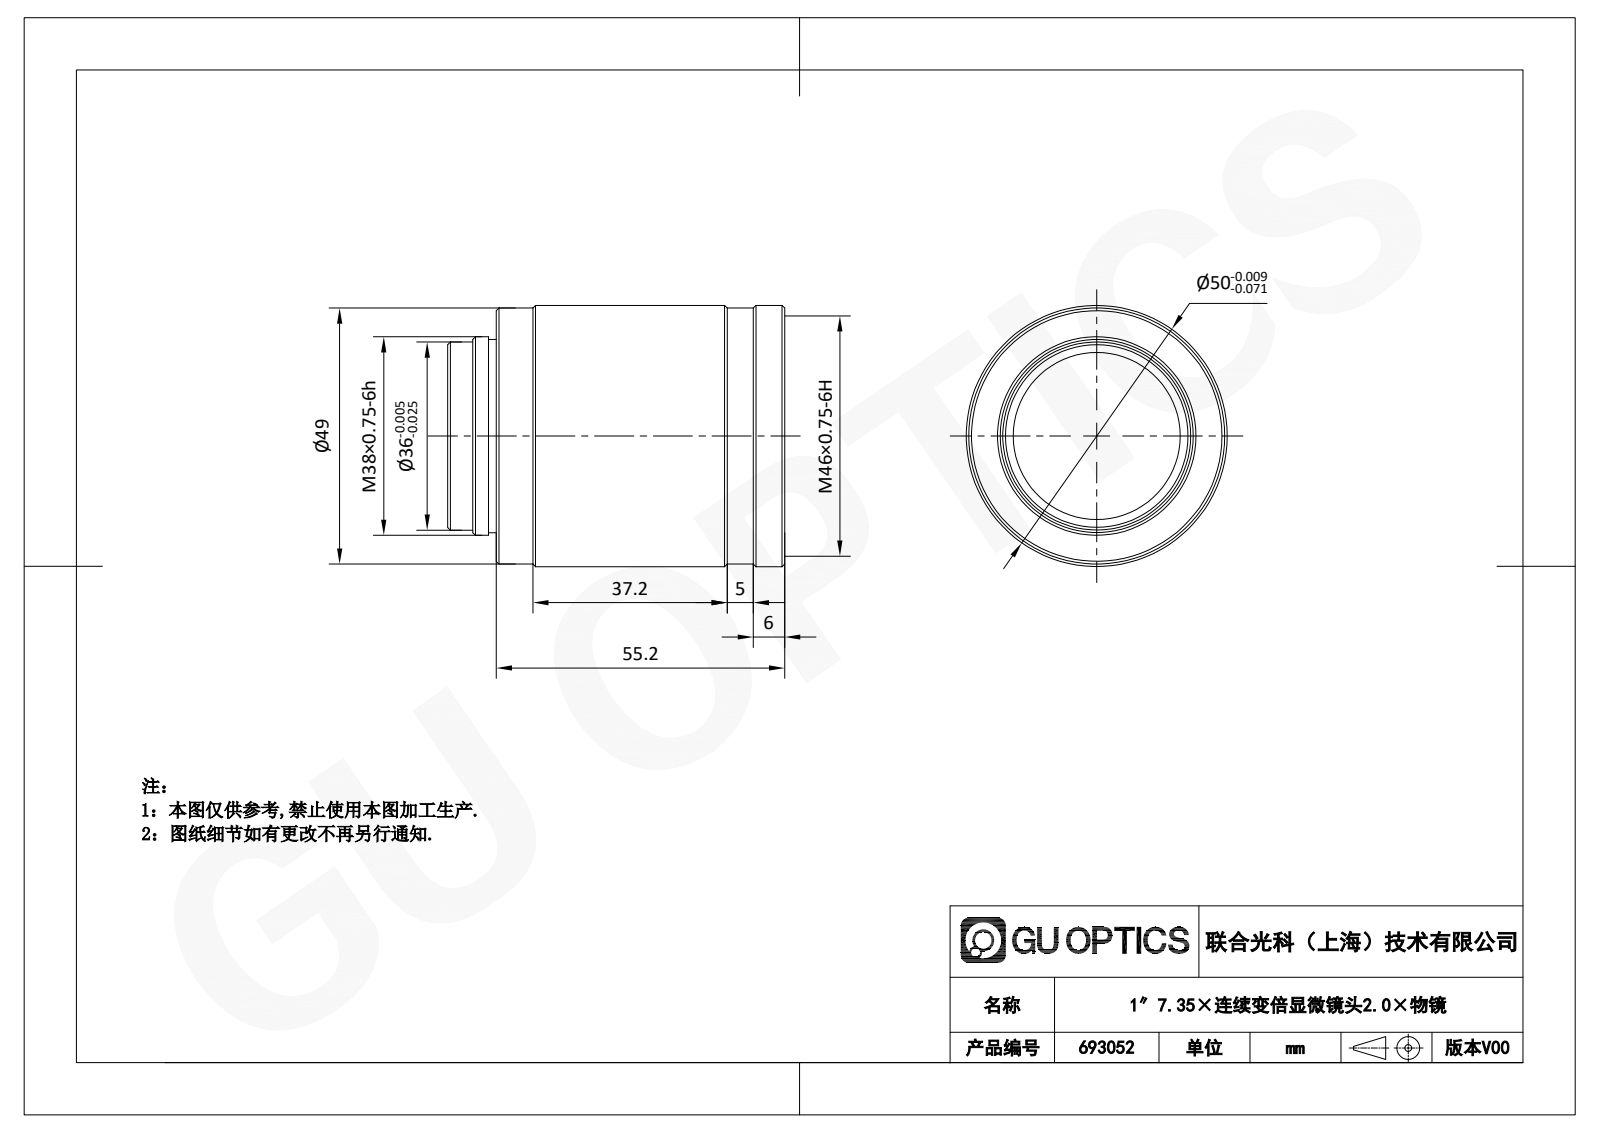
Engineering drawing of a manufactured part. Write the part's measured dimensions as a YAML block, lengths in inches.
part_name: "693052"
step_written_by: "SolidWorks 2020 (CONFIG_CONTROL_DESIGN)"
units: inches
bodies: {solids: 1, faces: 23, planar: 5, cylindrical: 9, other: 9}
overall_size: [2.539, 1.969, 1.969]
volume: 6.882
surface_area: 22
round_holes:
  - {diameter: 1.26, count: 1}
  - {diameter: 1.811, count: 1}
round_bosses_or_shafts:
  - {diameter: 1.969, count: 1}
  - {diameter: 1.929, count: 1}
  - {diameter: 1.496, count: 1}
  - {diameter: 1.457, count: 1}
  - {diameter: 1.417, count: 1}
face_to_face_distances: [2.173, 2.539, 0.366, 2.232, 0.059, 0.307, 2.35, 0.177, 0.118, 0.189]
